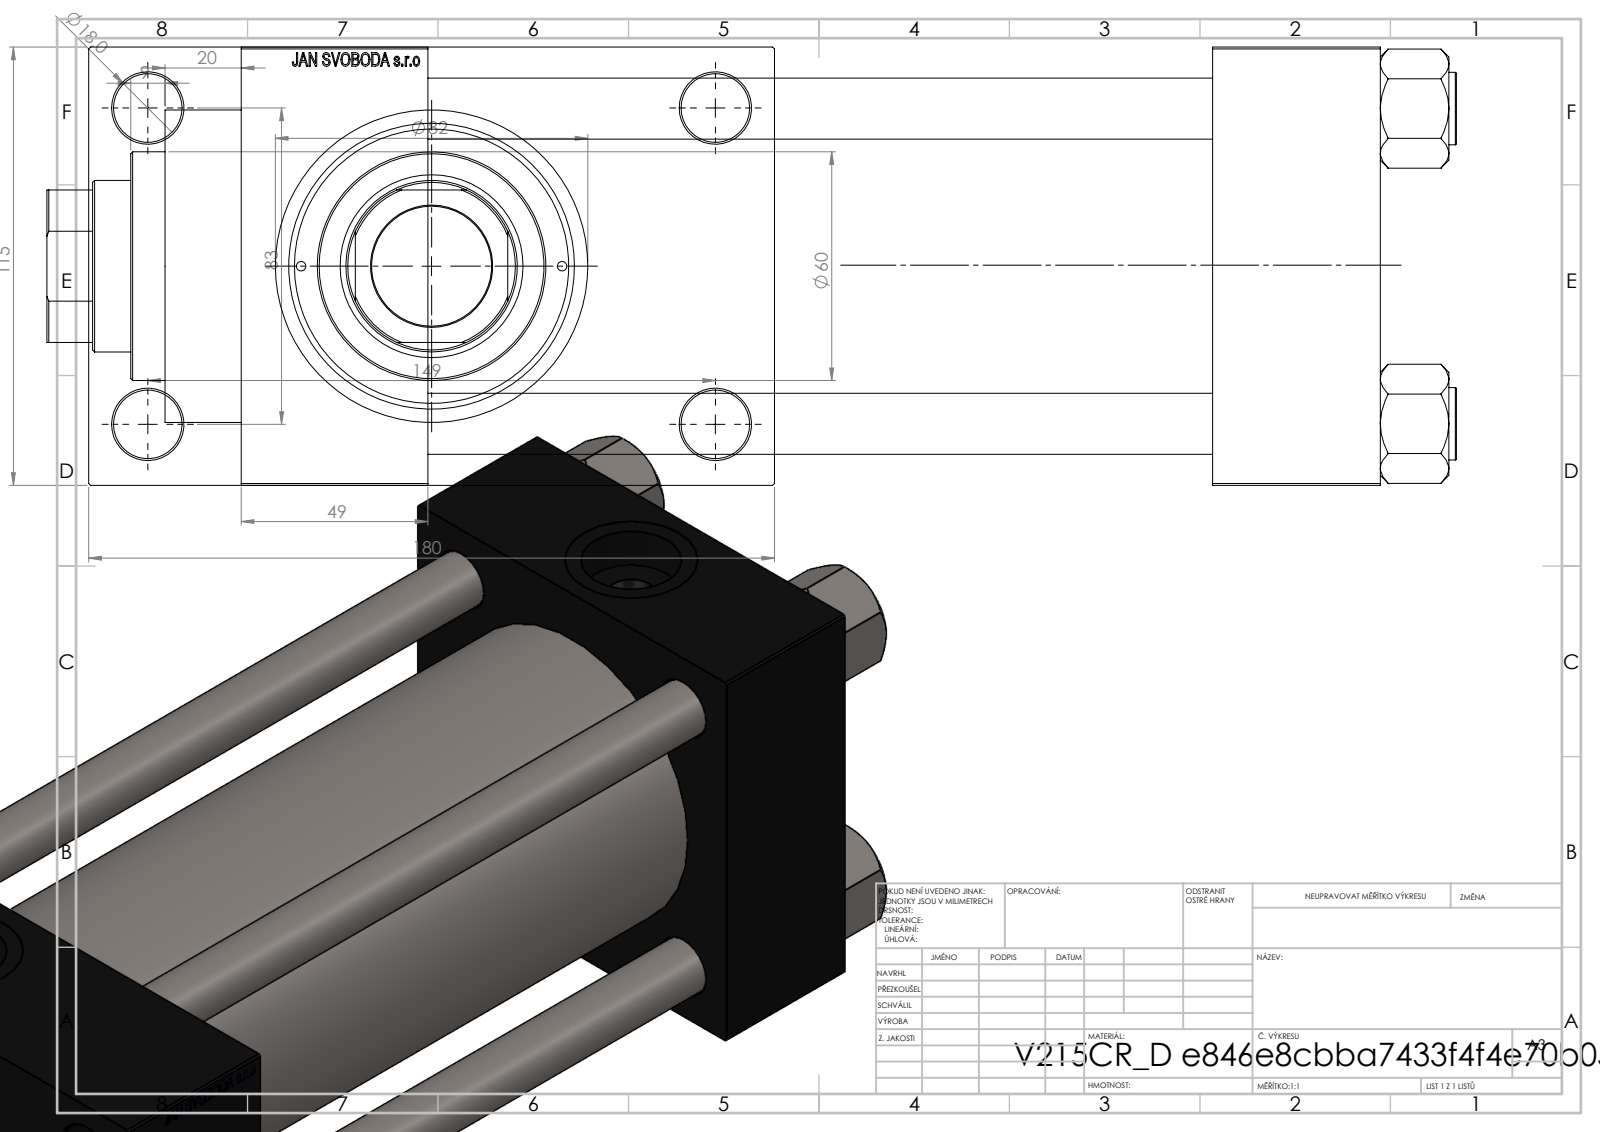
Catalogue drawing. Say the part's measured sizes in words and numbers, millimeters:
The part is named "NUT_M5_D; V215CR_D_TYCINKA; V215_VC_A; V215CR_D_Body (+1 more)". Its 3-D file was written by "SolidWorks 2019 (CONFIG_CONTROL_DESIGN)". It is 11 solids with 1160 faces: 547 planar, 93 cylindrical and 520 other. Overall it measures 370 by 180 by 115 millimeters. Its volume is 2 466 000 cubic millimeters and its surface area 420 592 square millimeters. Round holes: 4 of diameter 16, 4 of diameter 18, 2 of diameter 2.5, 2 of diameter 7, 2 of diameter 26.44, 2 of diameter 35, 1 of diameter 31.5, 1 of diameter 45, 1 of diameter 48, 1 of diameter 61, 1 of diameter 72, 1 of diameter 80. Round bosses or shafts: 4 of diameter 19, 1 of diameter 86, 1 of diameter 82, 1 of diameter 60. Partial cylindrical surfaces (rounded edges, fillets, slot ends): 1 of radius 22. The main face-to-face distances are 115, 206, 255, 49, 44, 250, 299, 32.5, 147.5, 180. The hole center spacings are 33.15, 41.96, 57.81, 58.48, 82.7, 85.28, 86.17, 89.24.
